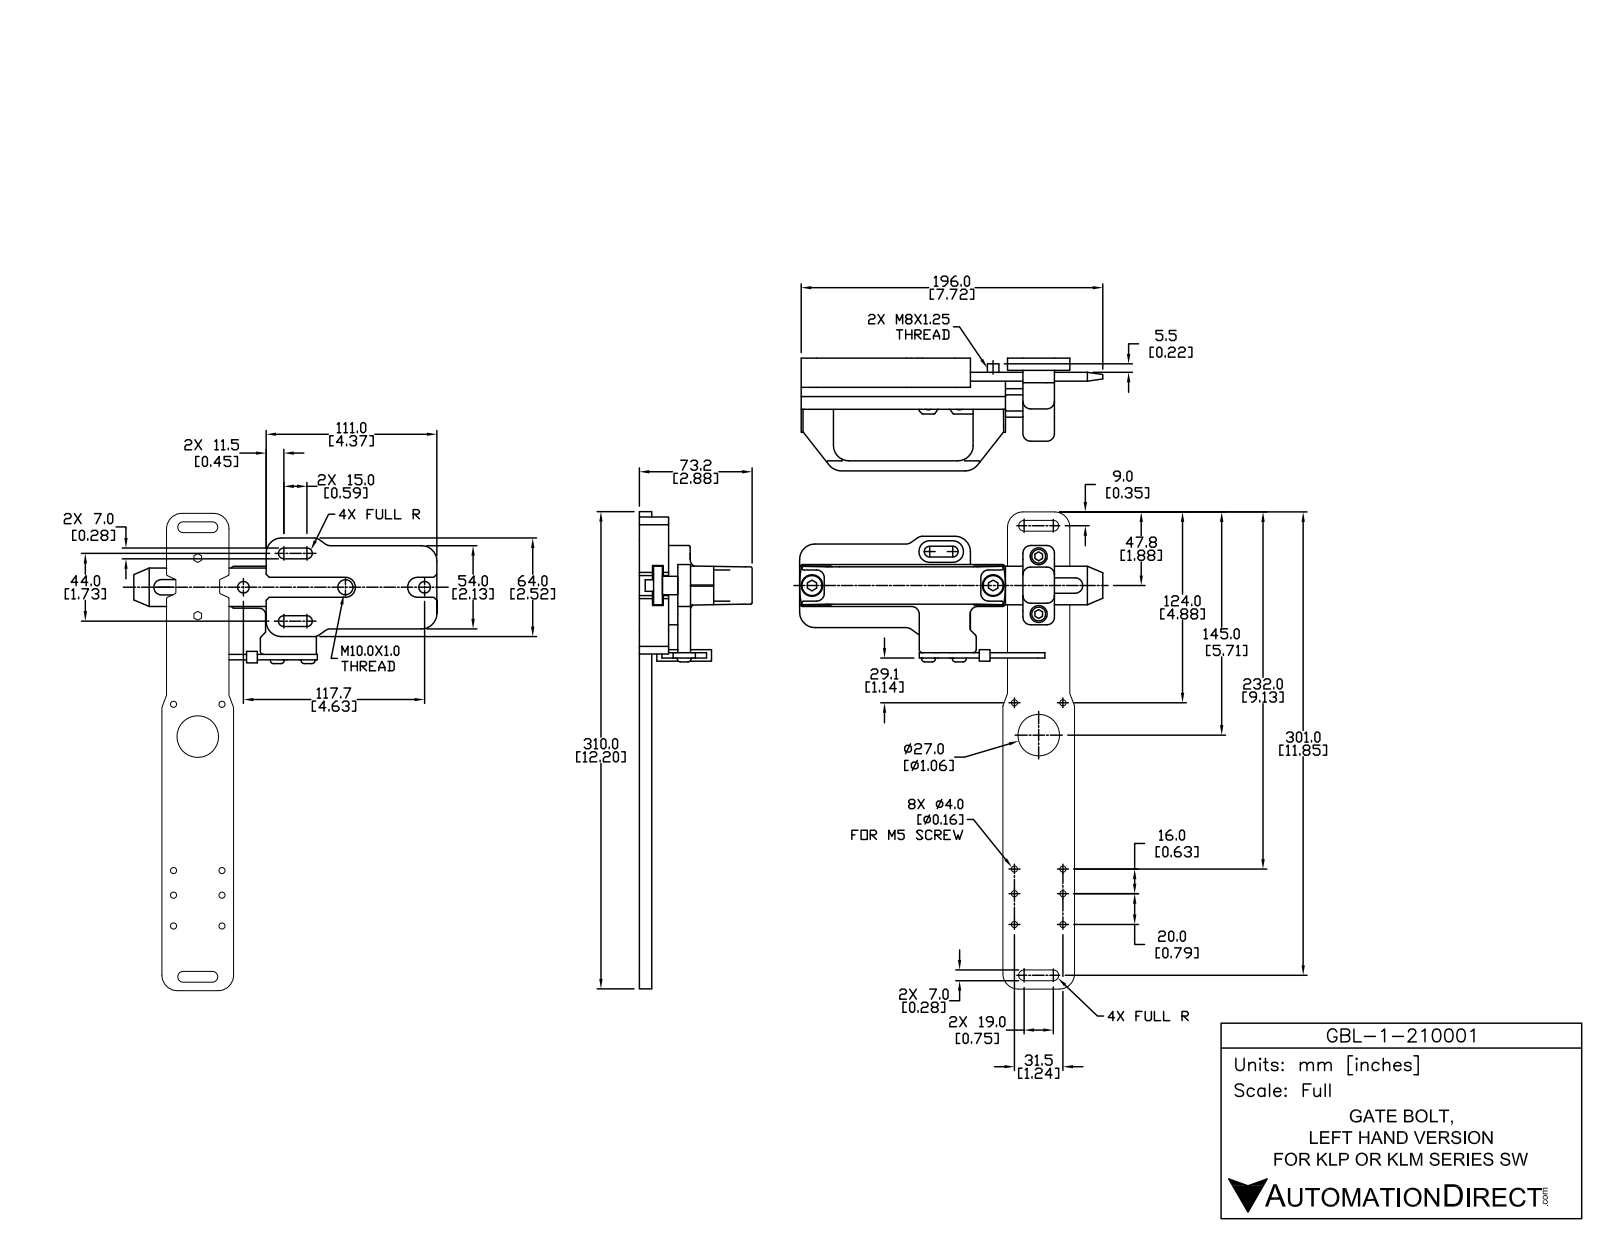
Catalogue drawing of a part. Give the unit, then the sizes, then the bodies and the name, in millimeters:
Units: millimetres
Overall size (bounding box): 310 × 251.1 × 78.8
Round holes (diameter × count): ⌀4 ×8, ⌀4.2 ×2, ⌀5 ×2, ⌀5.5 ×2, ⌀6.5 ×2, ⌀6.75 ×2, ⌀8.3 ×2, ⌀8.6 ×2, ⌀8.8 ×2, ⌀11 ×2, ⌀14 ×2, ⌀9 ×1
Round bosses / shafts (diameter × count): ⌀13 ×2, ⌀10 ×2, ⌀9.3 ×2, ⌀8 ×2, ⌀6 ×2, ⌀5 ×2
Partial cylindrical surfaces — rounded edges, fillets, slot ends (radius × count): R0.5 ×110, R0.1 ×56, R1 ×38, R3 ×16, R5 ×16, R2 ×14, R8 ×8, R3.45 ×6
Main face-to-face distances: 8, 23.8, 19, 10, 6, 7.8, 16, 15.8, 13.8, 5.8
Hole centre spacings: 30, 202.56, 20, 36, 16, 26.22, 34, 36.06
Volume: 327 401 mm³ · Surface area: 122 453 mm²
Bodies: 15 solids, 875 faces (316 planar, 358 cylindrical, 201 other)
Part name (STEP PRODUCT): GBL-1-210001
STEP written by: SolidWorks 2019 (AUTOMOTIVE_DESIGN)
